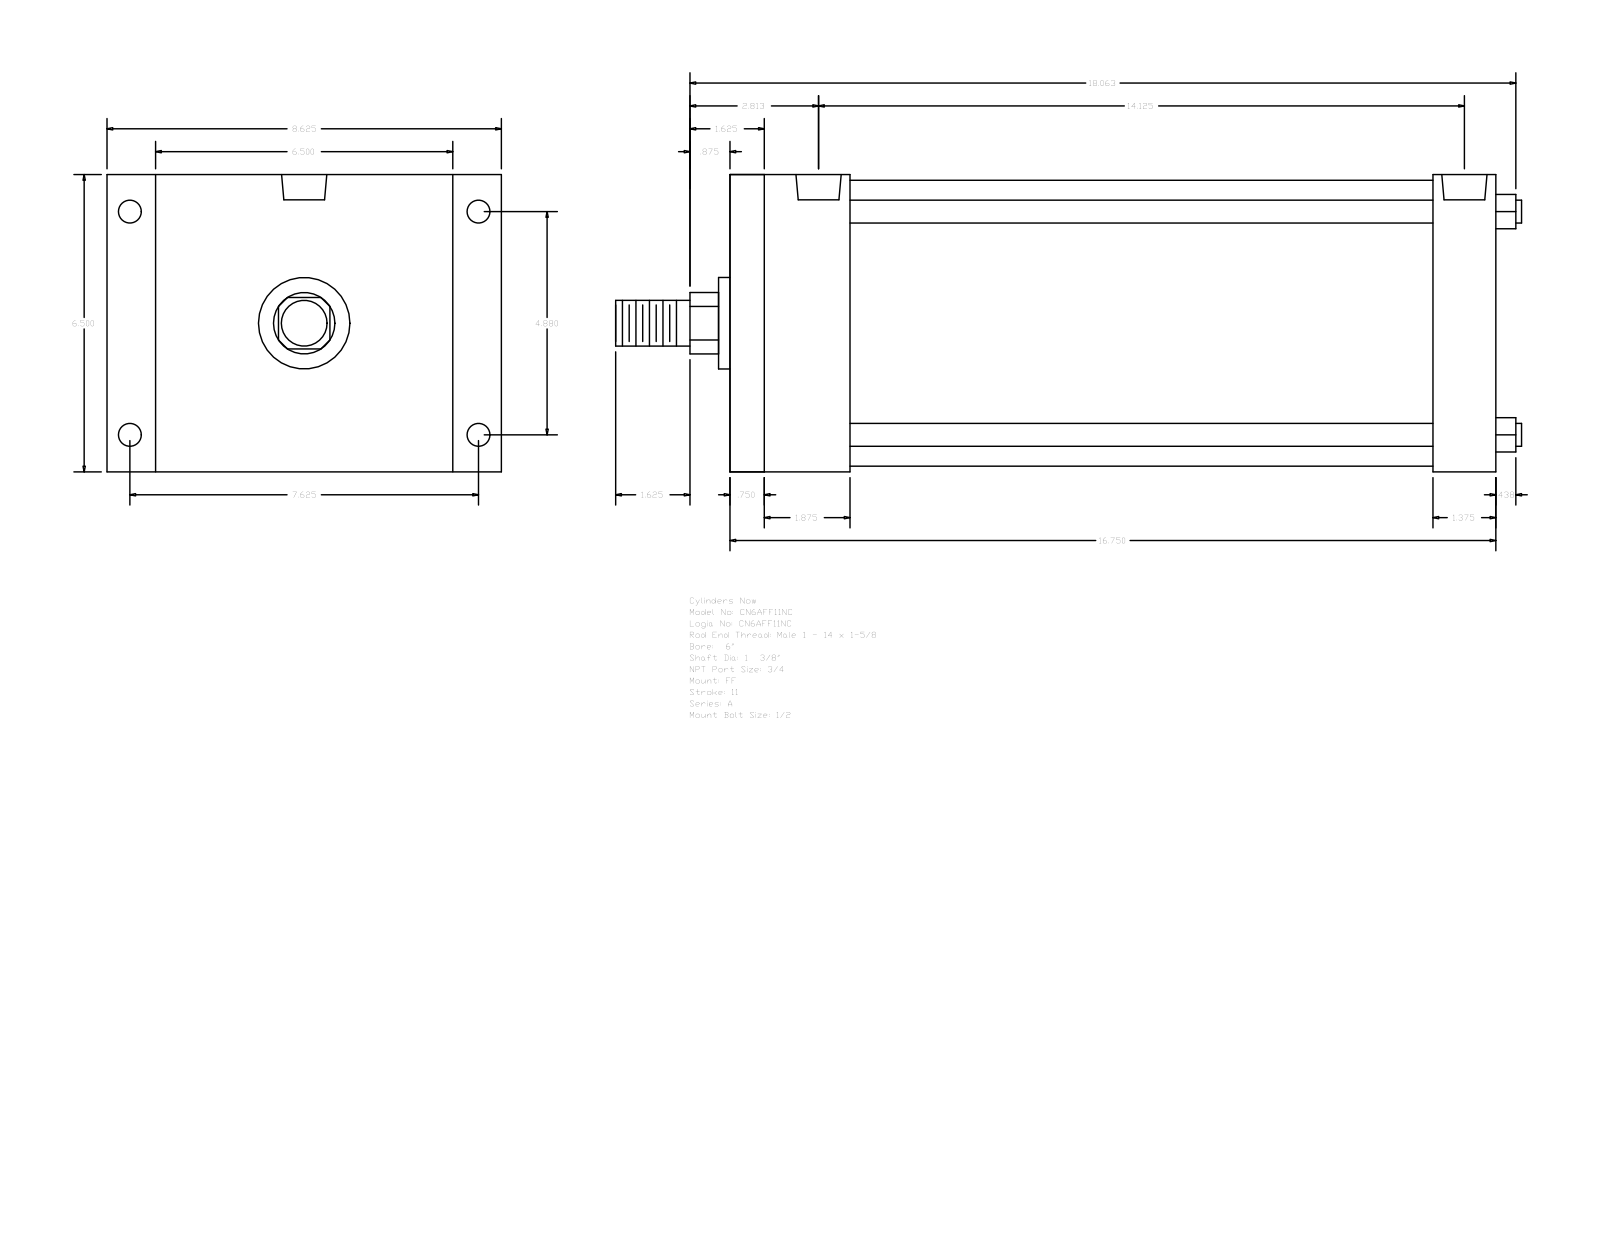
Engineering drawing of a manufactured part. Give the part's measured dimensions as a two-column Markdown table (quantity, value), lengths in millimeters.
| quantity | value |
| --- | --- |
| part name | A_FF__0600_1.375 |
| STEP written by | GSSL Pune (CONFIG_CONTROL_DESIGN) |
| units | millimeters |
| bodies | 0 solids, 92 faces (64 planar, 28 cylindrical, 0 other) |
| overall size | 503.24 × 219.07 × 165.1 |
| round holes (diameter × count) | 12.7 × 4, 15.08 × 4, 25.12 × 2 |
| round bosses / shafts (diameter × count) | 12.7 × 4, 158.75 × 1, 50.8 × 1, 34.92 × 1, 25.4 × 1 |
| partial cylindrical surfaces (radius × count) | 17.06 × 1 |
| main face-to-face distances | 165.1, 425.45, 19.04, 406.41, 66.67, 47.63, 358.78, 390.52, 371.48, 323.85 |
| hole center spacings | 5.56, 123.96, 193.68, 229.95, 347.65, 353.21, 358.77 |
